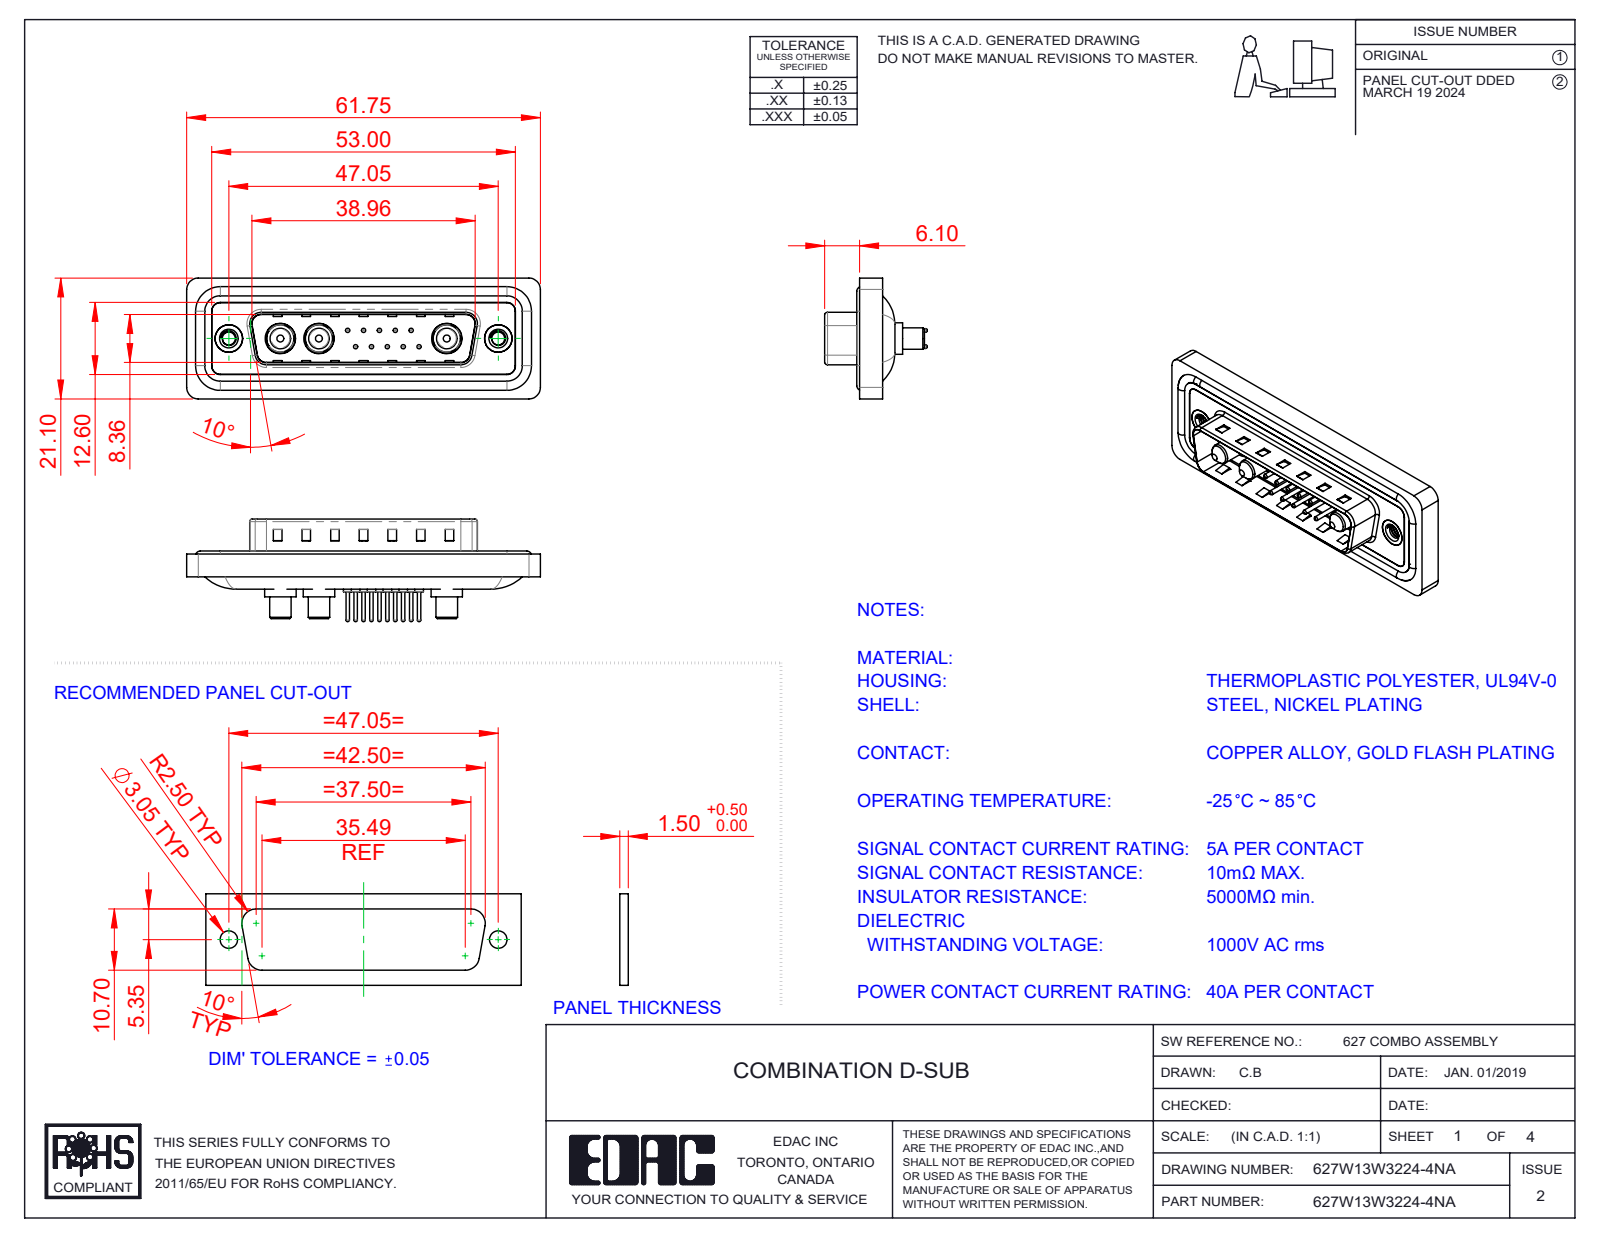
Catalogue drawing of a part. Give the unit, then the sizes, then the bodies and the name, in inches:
Units: inches
Overall size (bounding box): 2.431 × 0.831 × 0.705
Round holes (diameter × count): ⌀0.03 ×10, ⌀0.063 ×10, ⌀0.079 ×10, ⌀0.191 ×3, ⌀0.209 ×3, ⌀0.089 ×2, ⌀0.157 ×2, ⌀0.189 ×2, ⌀0.197 ×2
Round bosses / shafts (diameter × count): ⌀0.059 ×10, ⌀0.024 ×10, ⌀0.063 ×4, ⌀0.217 ×3, ⌀0.205 ×3, ⌀0.187 ×3, ⌀0.148 ×3, ⌀0.142 ×3
Partial cylindrical surfaces — rounded edges, fillets, slot ends (radius × count): R0.059 ×22, R0.079 ×18, R0.02 ×8, R0.063 ×8, R0.01 ×4, R0.024 ×4, R0.026 ×4, R0.035 ×4
Main face-to-face distances: 0.016, 0.059, 0.043, 0.063, 0.02, 0.122, 0.114, 0.032, 0.377, 0.161
Hole centre spacings: 0.124, 0.109, 0.198, 0.218, 0.295, 0.198, 0.327, 0.398
Volume: 0.451 in³ · Surface area: 18.45 in²
Bodies: 23 solids, 968 faces (309 planar, 387 cylindrical, 272 other)
Part name (STEP PRODUCT): Power Pin_40A S; 627W13W3224-4NA; 627Combo Shell Rear_25 Contacts; 627Combo Contact Row 1_24 (+5 more)
STEP written by: SolidWorks 2023 (CONFIG_CONTROL_DESIGN)
